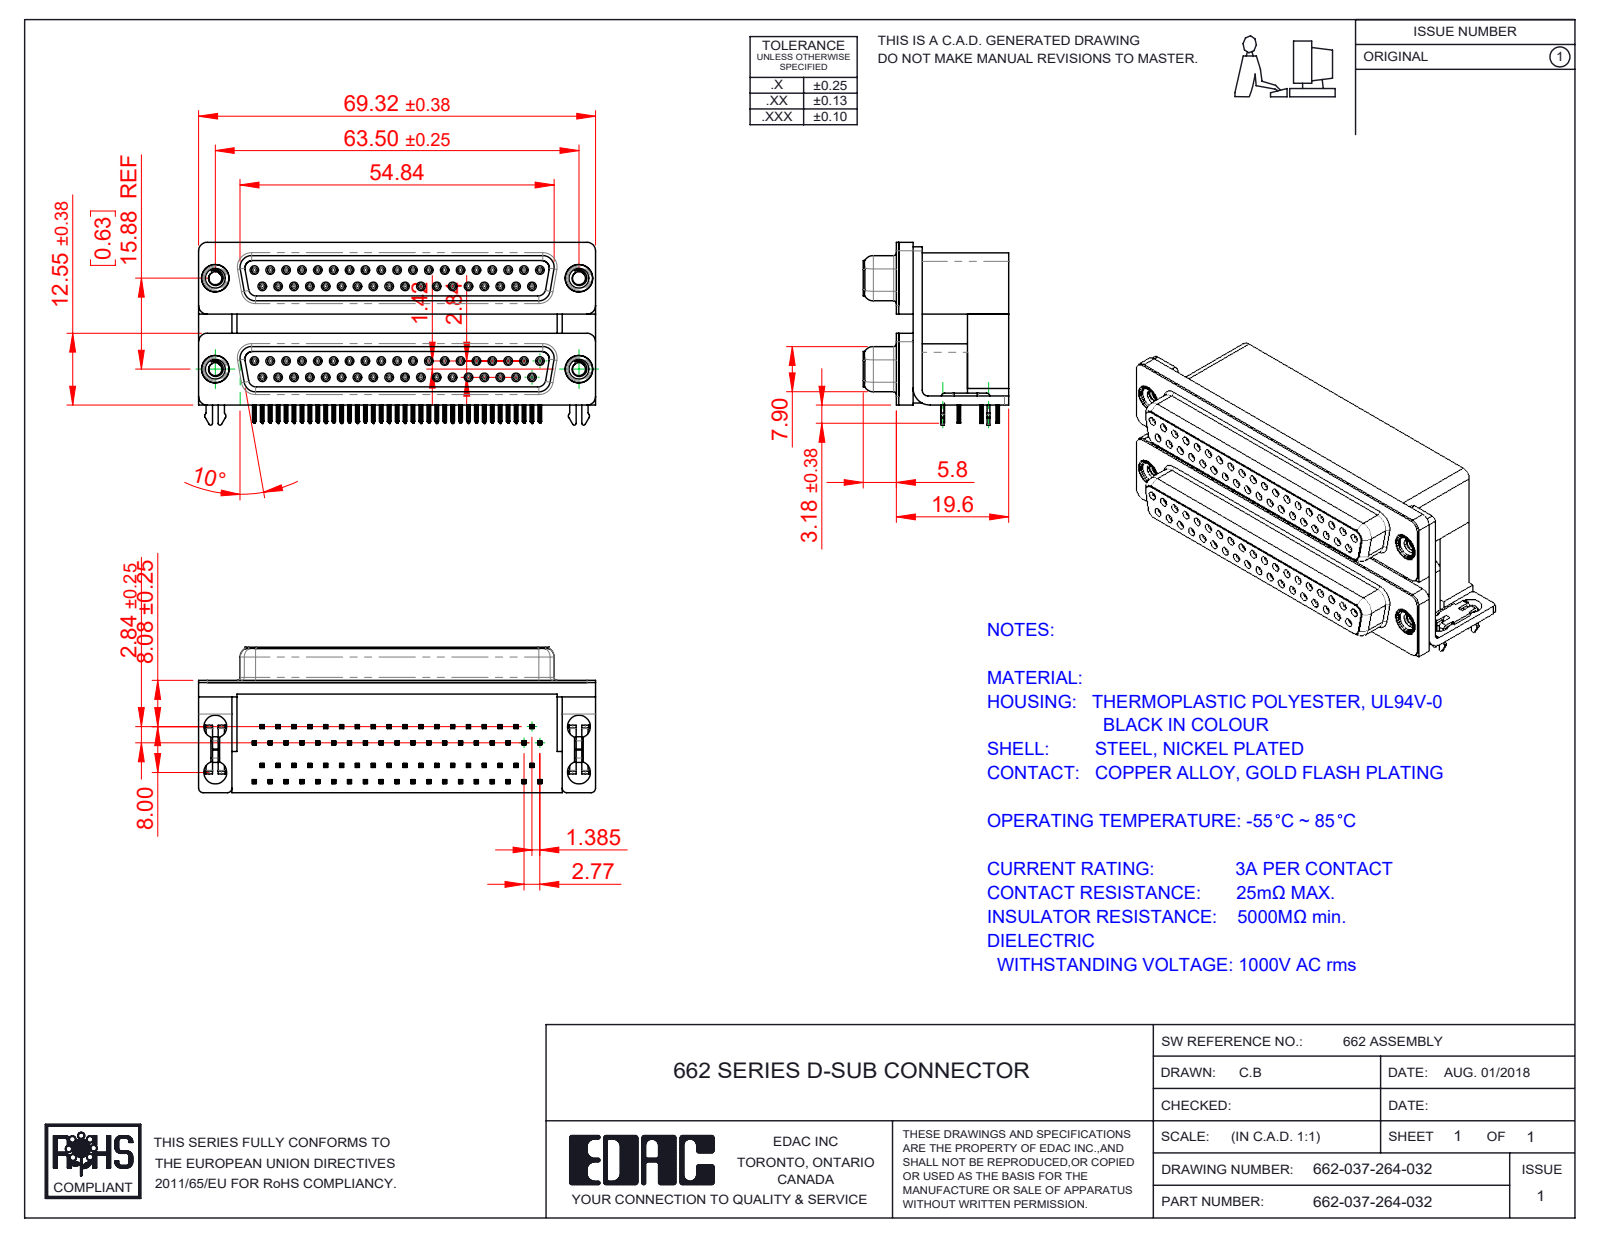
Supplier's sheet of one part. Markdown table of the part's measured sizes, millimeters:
| quantity | value |
| --- | --- |
| part name | 662 Mounting Bracket_2ProngL; 662 Housing Spacer_37 Contacts L; 662 Contact Bottom Upper_L; 662 Housing Lower_37 Contacts (+8 more) |
| STEP written by | SolidWorks 2020 (CONFIG_CONTROL_DESIGN) |
| units | millimeters |
| bodies | 87 solids, 11460 faces (5334 planar, 2610 cylindrical, 3516 other) |
| overall size | 69.32 × 31.93 × 25.4 |
| volume | 31 775 mm³ |
| surface area | 34 329 mm² |
| round holes (diameter × count) | 0.8 × 74, 0.9 × 74, 4 × 8, 2.26 × 4, 3.5 × 4, 4.8 × 4, 5 × 4 |
| round bosses / shafts (diameter × count) | 1.2 × 74, 4.9 × 4, 4.75 × 4, 3.9 × 4 |
| partial cylindrical surfaces (radius × count) | 0.1 × 594, 0.15 × 296, 0.35 × 148, 0.34 × 74, 0.28 × 36, 1.35 × 18, 0.5 × 12, 1.5 × 12 |
| main face-to-face distances | 0.4, 19.2, 15.88, 7.2, 12, 6.2, 15.52, 2.84, 26.22, 10.7 |
| hole center spacings | 3.16, 2.77, 5.54, 8.31, 11.08, 22.16, 13.85, 19.39 |
